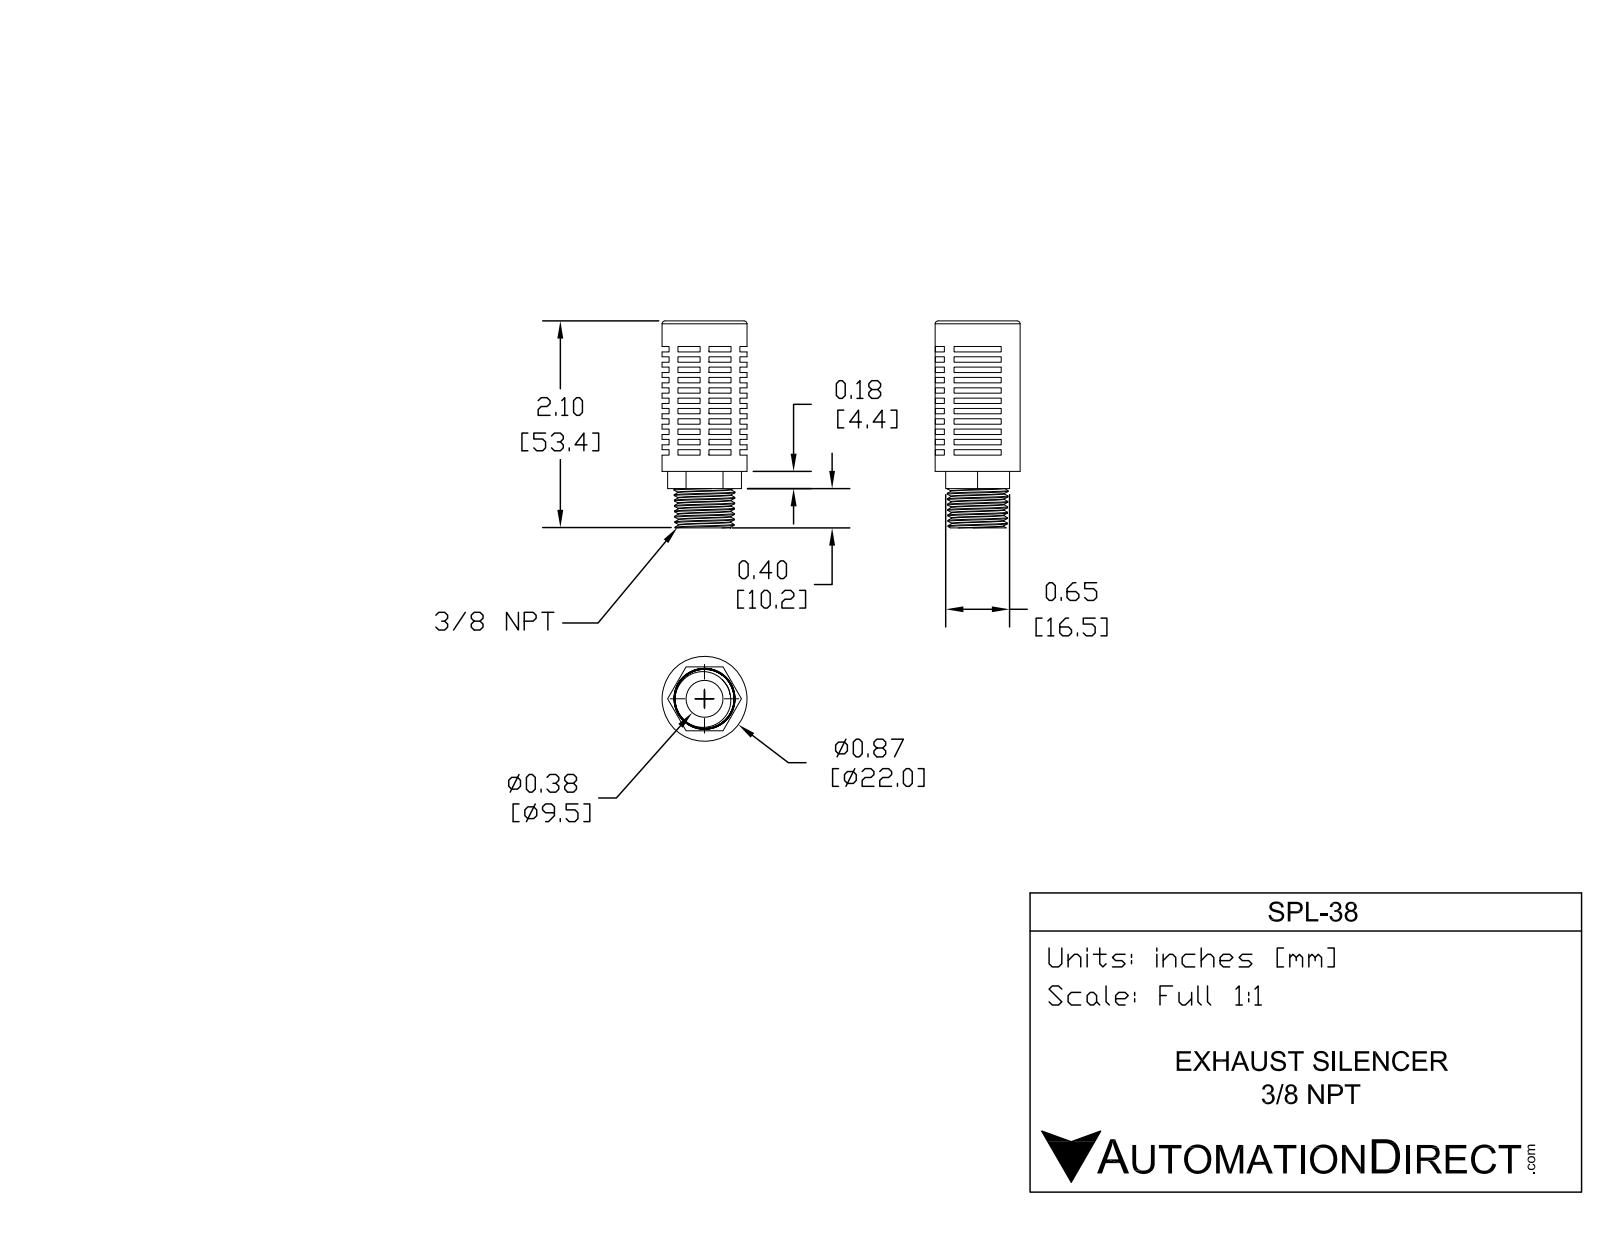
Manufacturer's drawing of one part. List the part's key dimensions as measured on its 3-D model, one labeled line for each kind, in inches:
Part name (STEP PRODUCT): SPL-38N
STEP written by: SolidWorks 2015 (CONFIG_CONTROL_DESIGN)
Units: inches
Bodies: 1 solid, 236 faces (210 planar, 4 cylindrical, 22 other)
Overall size (bounding box): 2.095 × 0.865 × 0.865
Volume: 0.691 in³ · Surface area: 15.56 in²
Round holes (diameter × count): ⌀0.375 ×1
Round bosses / shafts (diameter × count): ⌀0.865 ×1
Main face-to-face distances: 0.315, 0.105, 0.42, 0.21, 0.63, 0.365, 0.05, 0.055, 0.21, 0.26
